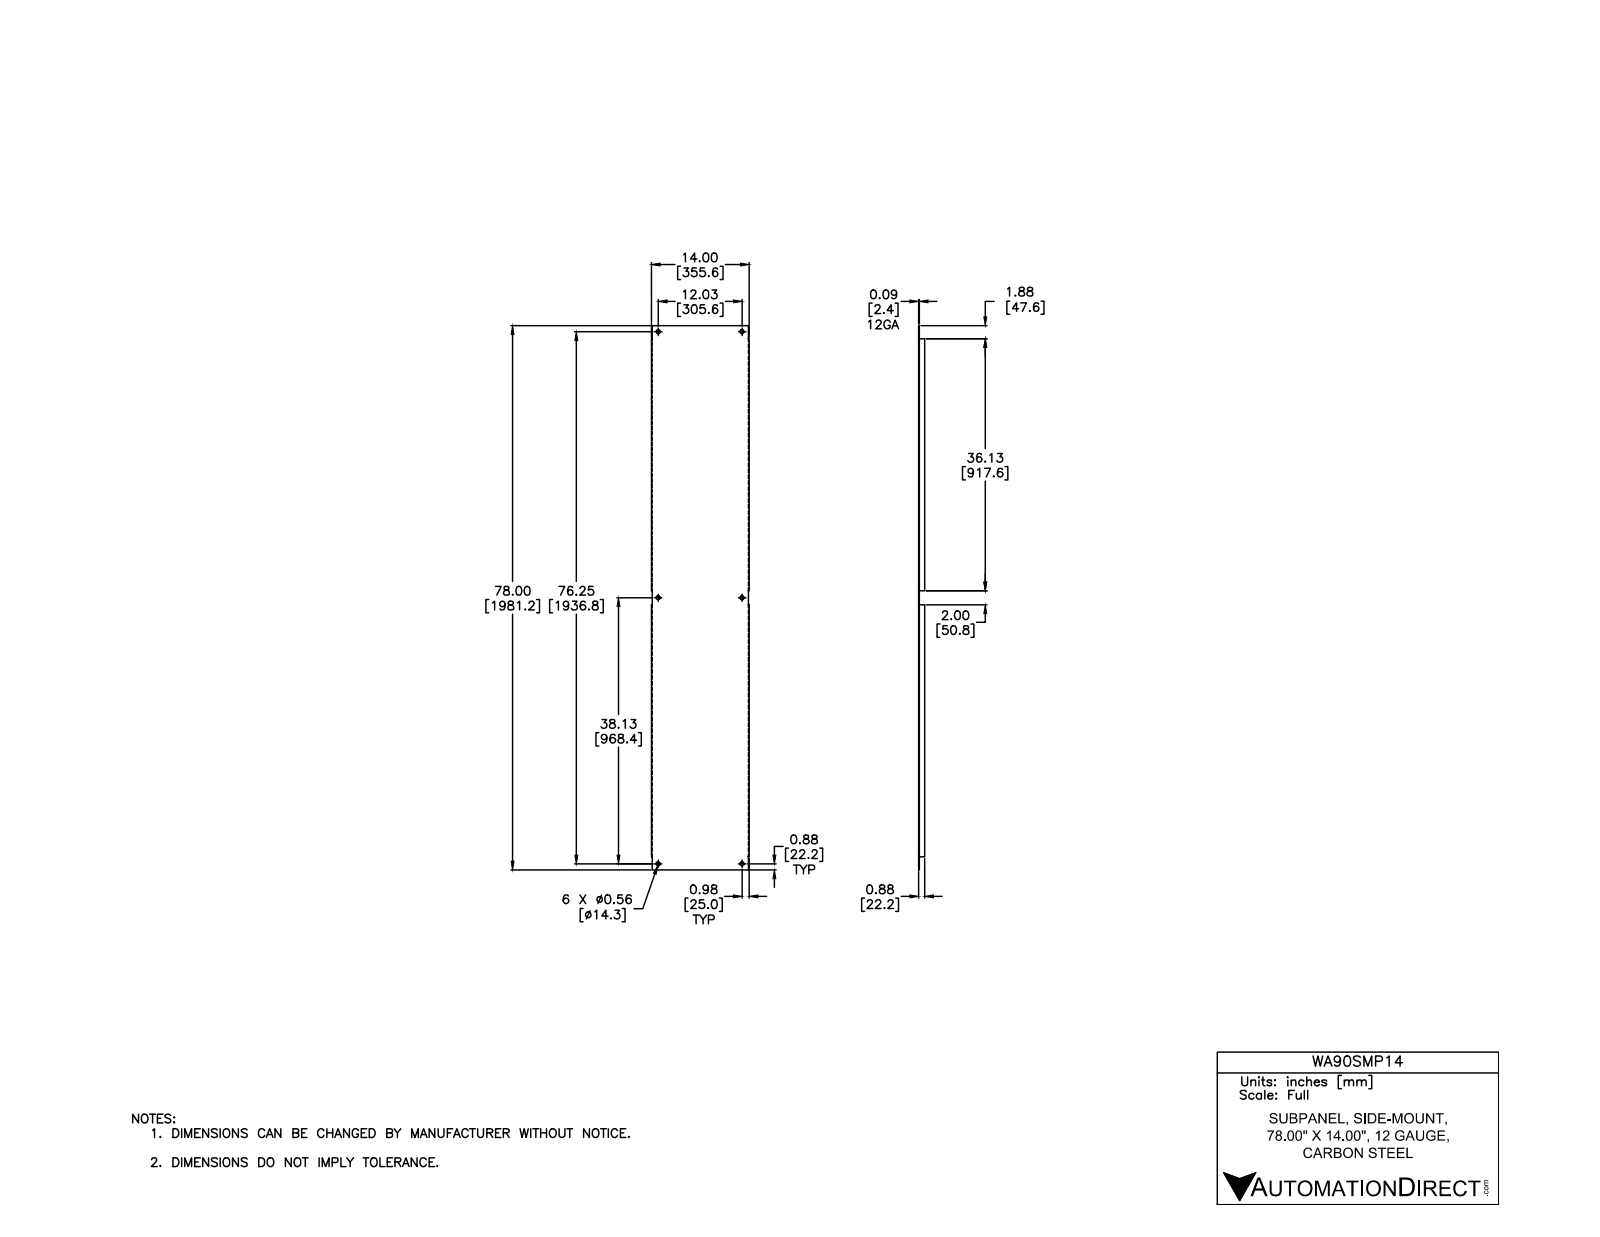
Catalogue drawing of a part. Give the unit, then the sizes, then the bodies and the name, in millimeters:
Units: millimetres
Overall size (bounding box): 1981.2 × 355.6 × 22.2
Round holes (diameter × count): ⌀14.3 ×6
Partial cylindrical surfaces — rounded edges, fillets, slot ends (radius × count): R0.4 ×2, R2.8 ×2
Main face-to-face distances: 2.4, 353.2, 350.9, 355.6, 19.8, 22.2, 1981.2, 2.8, 352.8, 0.4
Hole centre spacings: 968.4, 1015.5, 305.6, 1936.8, 1960.7
Volume: 1 840 000 mm³ · Surface area: 1 558 000 mm²
Bodies: 1 solid, 48 faces (34 planar, 14 cylindrical, 0 other)
Part name (STEP PRODUCT): WA60SMP14-WA90SMP20
STEP written by: Autodesk Inventor 2012 (AUTOMOTIVE_DESIGN)
